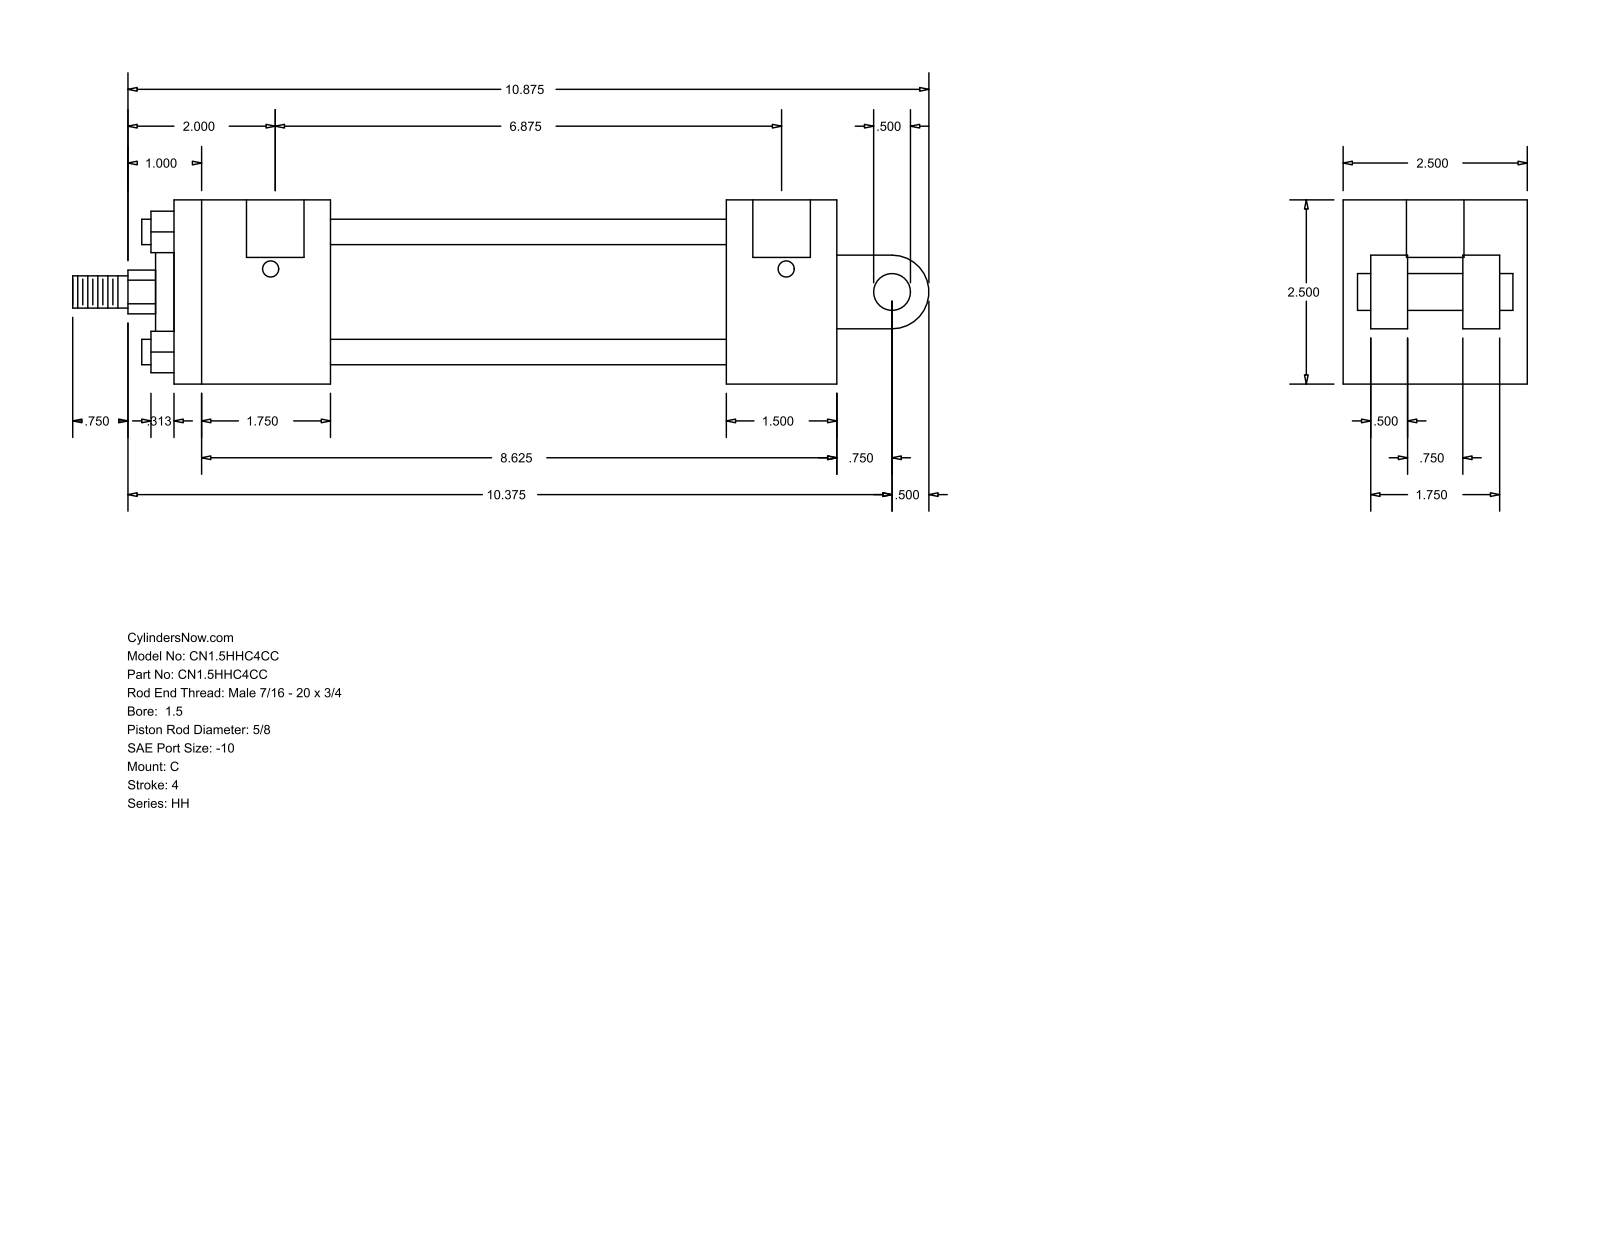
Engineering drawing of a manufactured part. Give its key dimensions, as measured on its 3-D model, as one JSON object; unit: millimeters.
{"part_name": "HH_C__0150_0.625", "step_written_by": "GSSL Pune (CONFIG_CONTROL_DESIGN)", "units": "millimeters", "bodies": {"solids": 0, "faces": 99, "planar": 70, "cylindrical": 29, "other": 0}, "overall_size": [295.27, 63.5, 63.5], "round_holes": [[5.56, 4], [19.84, 2]], "round_bosses_or_shafts": [[8.76, 4], [44.45, 1], [28.57, 1], [15.88, 1], [12.7, 1], [11.11, 1]], "partial_cylinders_radius": [[7.54, 1], [12.7, 1]], "face_to_face_distances": [63.5, 228.59, 53.97, 190.5, 136.53, 174.62, 38.09, 12.7, 19.05, 22.22], "hole_center_spacings": [177.8, 1.58, 1.59, 174.63, 176.21, 176.22]}
